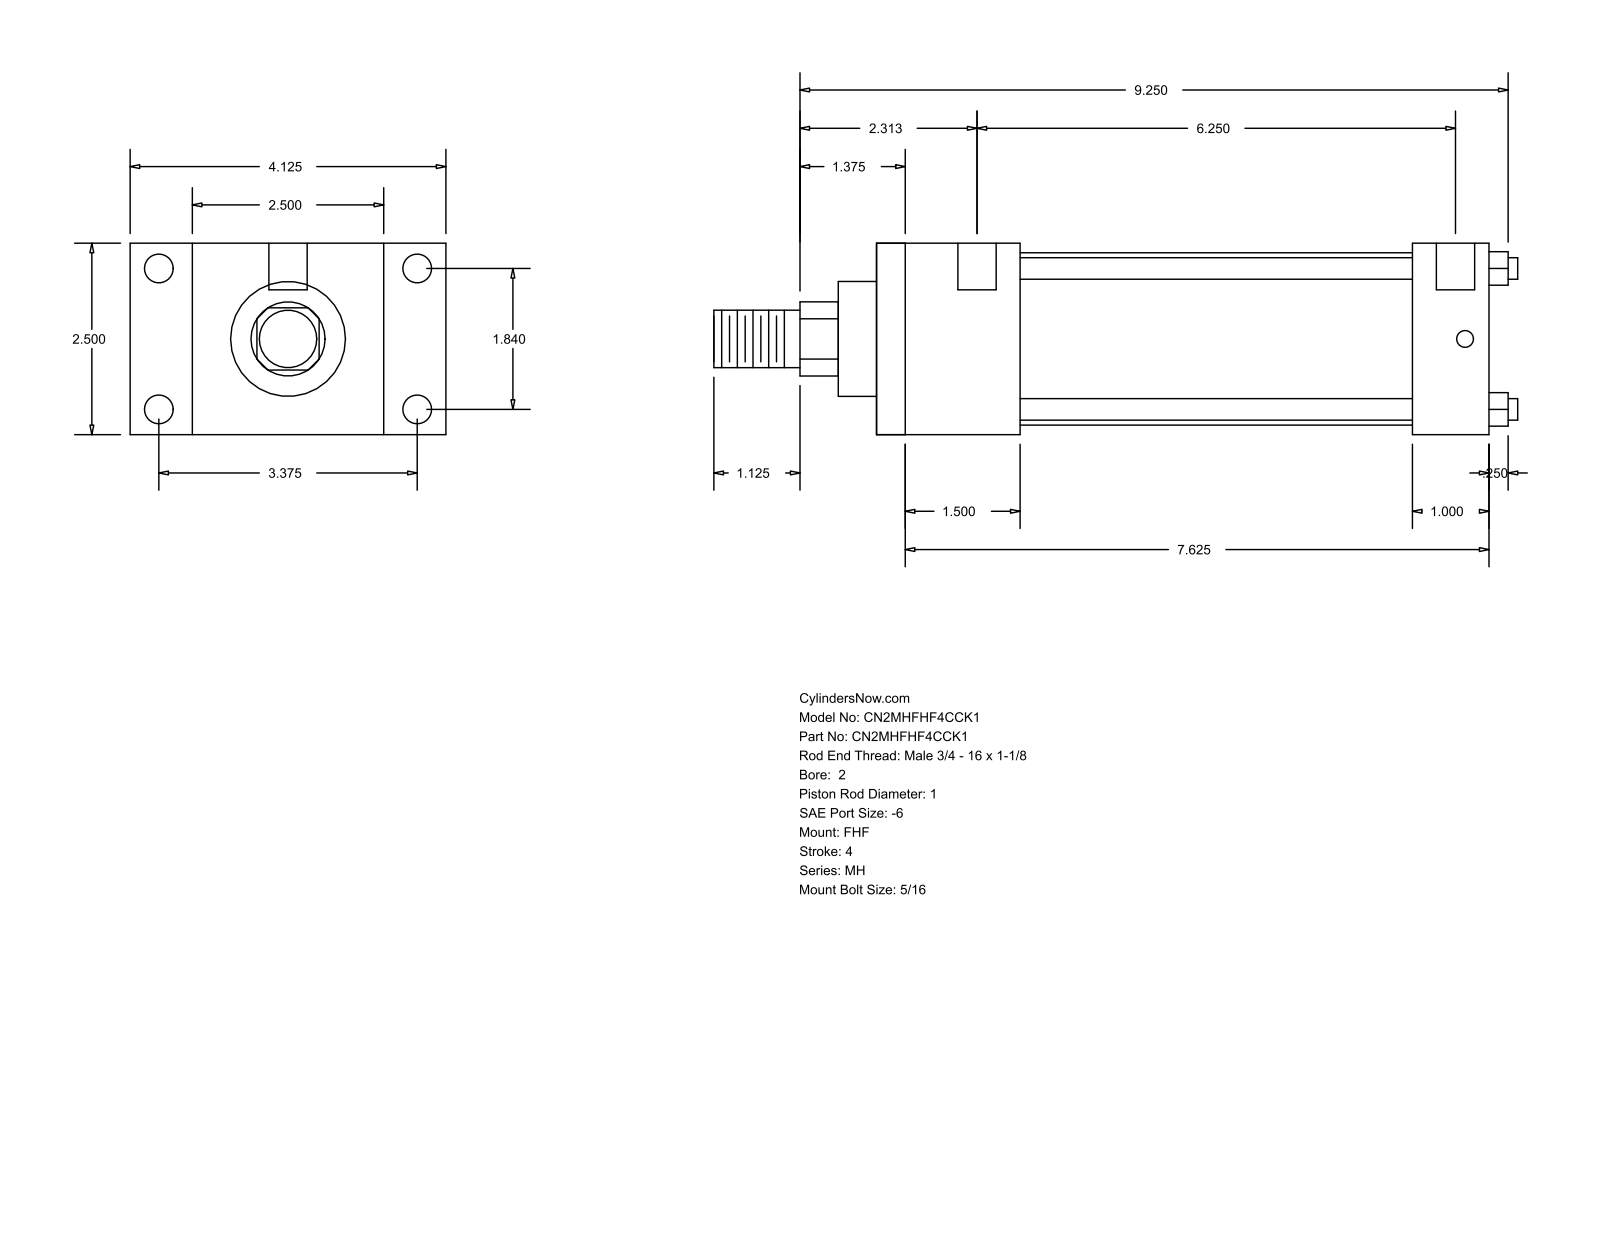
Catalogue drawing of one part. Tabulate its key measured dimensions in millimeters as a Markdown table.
| quantity | value |
| --- | --- |
| part name | MH_FHF__0200_1 |
| STEP written by | GSSL Pune (CONFIG_CONTROL_DESIGN) |
| units | millimeters |
| bodies | 0 solids, 88 faces (60 planar, 28 cylindrical, 0 other) |
| overall size | 266.7 × 104.78 × 63.5 |
| round holes (diameter × count) | 5.56 × 4, 9.53 × 4, 12.7 × 2 |
| round bosses / shafts (diameter × count) | 7.14 × 4, 57.15 × 1, 38.1 × 1, 25.4 × 1, 19.05 × 1 |
| partial cylindrical surfaces (radius × count) | 12.29 × 1 |
| main face-to-face distances | 63.5, 203.2, 47.63, 155.57, 20.64, 84.14, 104.78, 25.4, 177.8, 130.17 |
| hole center spacings | 46.74, 85.72, 97.63, 166.68, 3.17, 4.76, 158.75, 161.92 |
